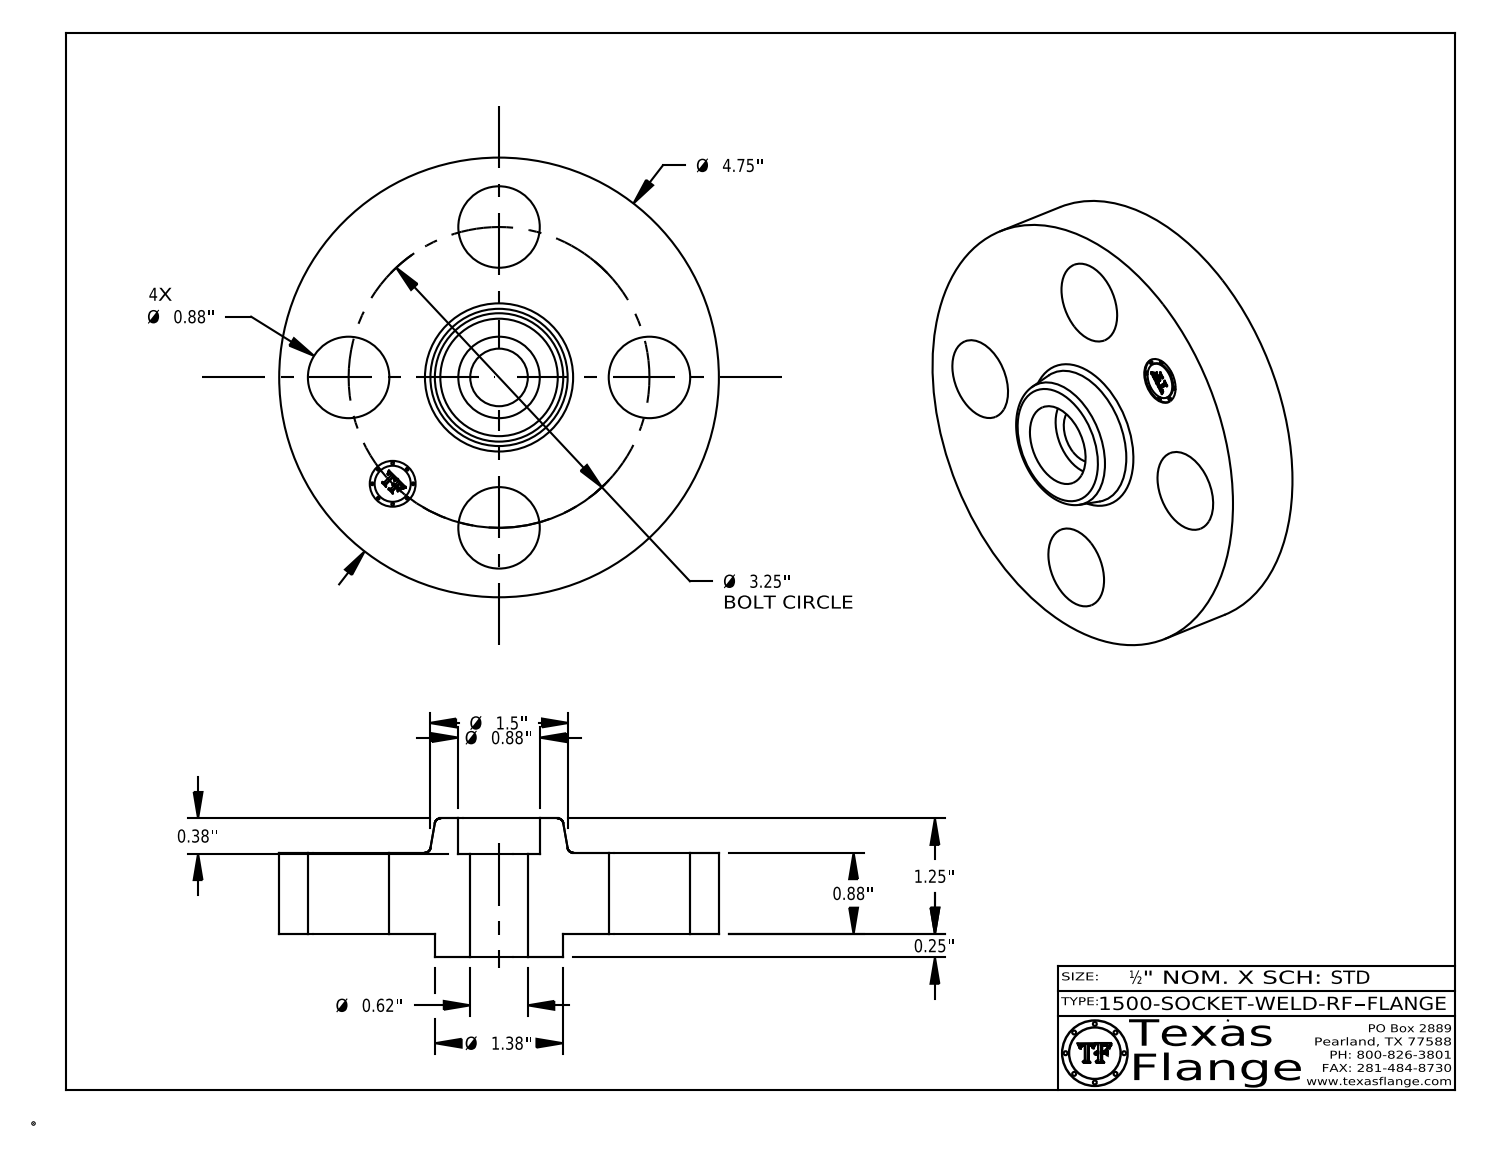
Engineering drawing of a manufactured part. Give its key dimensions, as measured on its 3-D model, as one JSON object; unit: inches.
{"part_name": "1500-SOCKET-WELD-RF", "step_written_by": "CATIA V5 STEP AP214 (AUTOMOTIVE_DESIGN)", "units": "inches", "bodies": {"solids": 1, "faces": 412, "planar": 370, "cylindrical": 36, "other": 6}, "overall_size": [4.75, 4.75, 1.5], "volume_in3": 13.85, "surface_area_in2": 58.49, "round_holes": [[0.88, 5], [0.495, 1], [0.622, 1]], "round_bosses_or_shafts": [[0.03, 8], [4.75, 1], [1.38, 1], [0.39, 1]], "face_to_face_distances": [0.88, 0.25, 1.13, 1.5, 1.25, 0.37, 1.12, 0.87, 0.38, 1.115], "hole_center_spacings": [1.625, 2.298, 1.244, 3.003, 3.25]}
